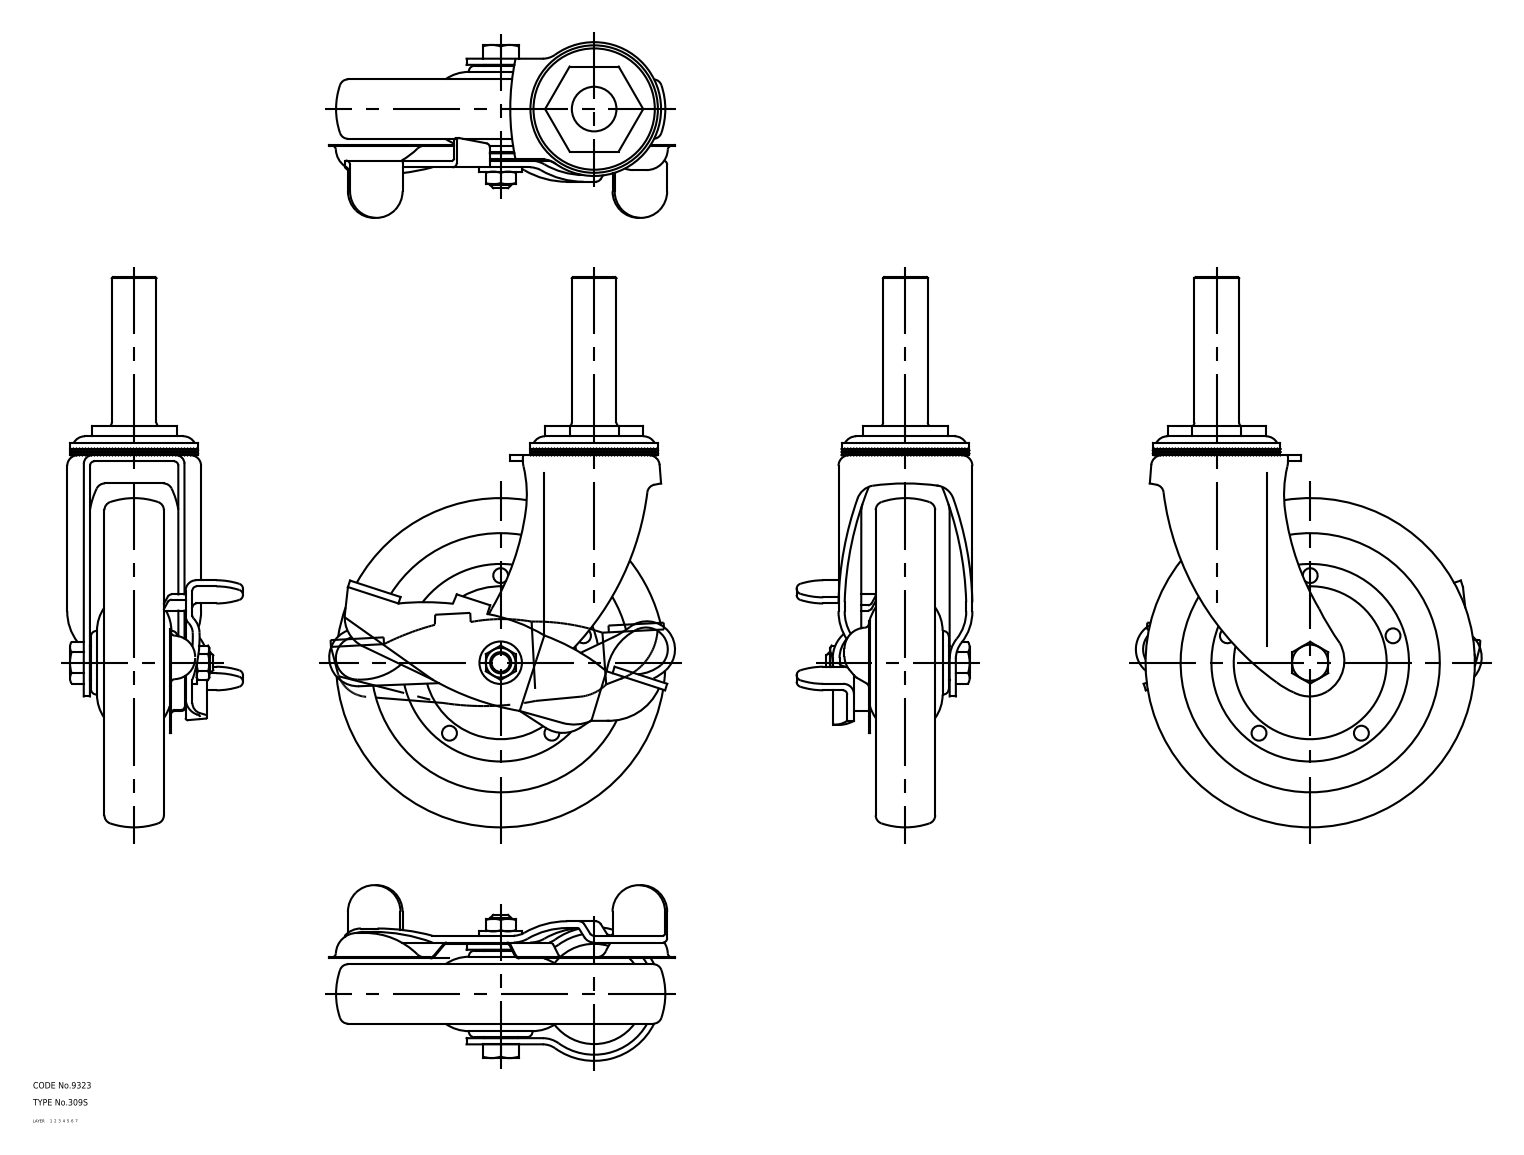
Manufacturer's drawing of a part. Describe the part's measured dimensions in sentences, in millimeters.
The part is named "67143942; 67143955; 67143968; 67143981 (+4 more)". Its 3-D file was written by "CADfix (AUTOMOTIVE_DESIGN)". It is 6 solids with 431 faces: 0 planar, 0 cylindrical and 431 other. Overall it measures 259 by 162.78 by 82.71 millimeters. Its volume is 574 883 cubic millimeters and its surface area 125 690 square millimeters.
